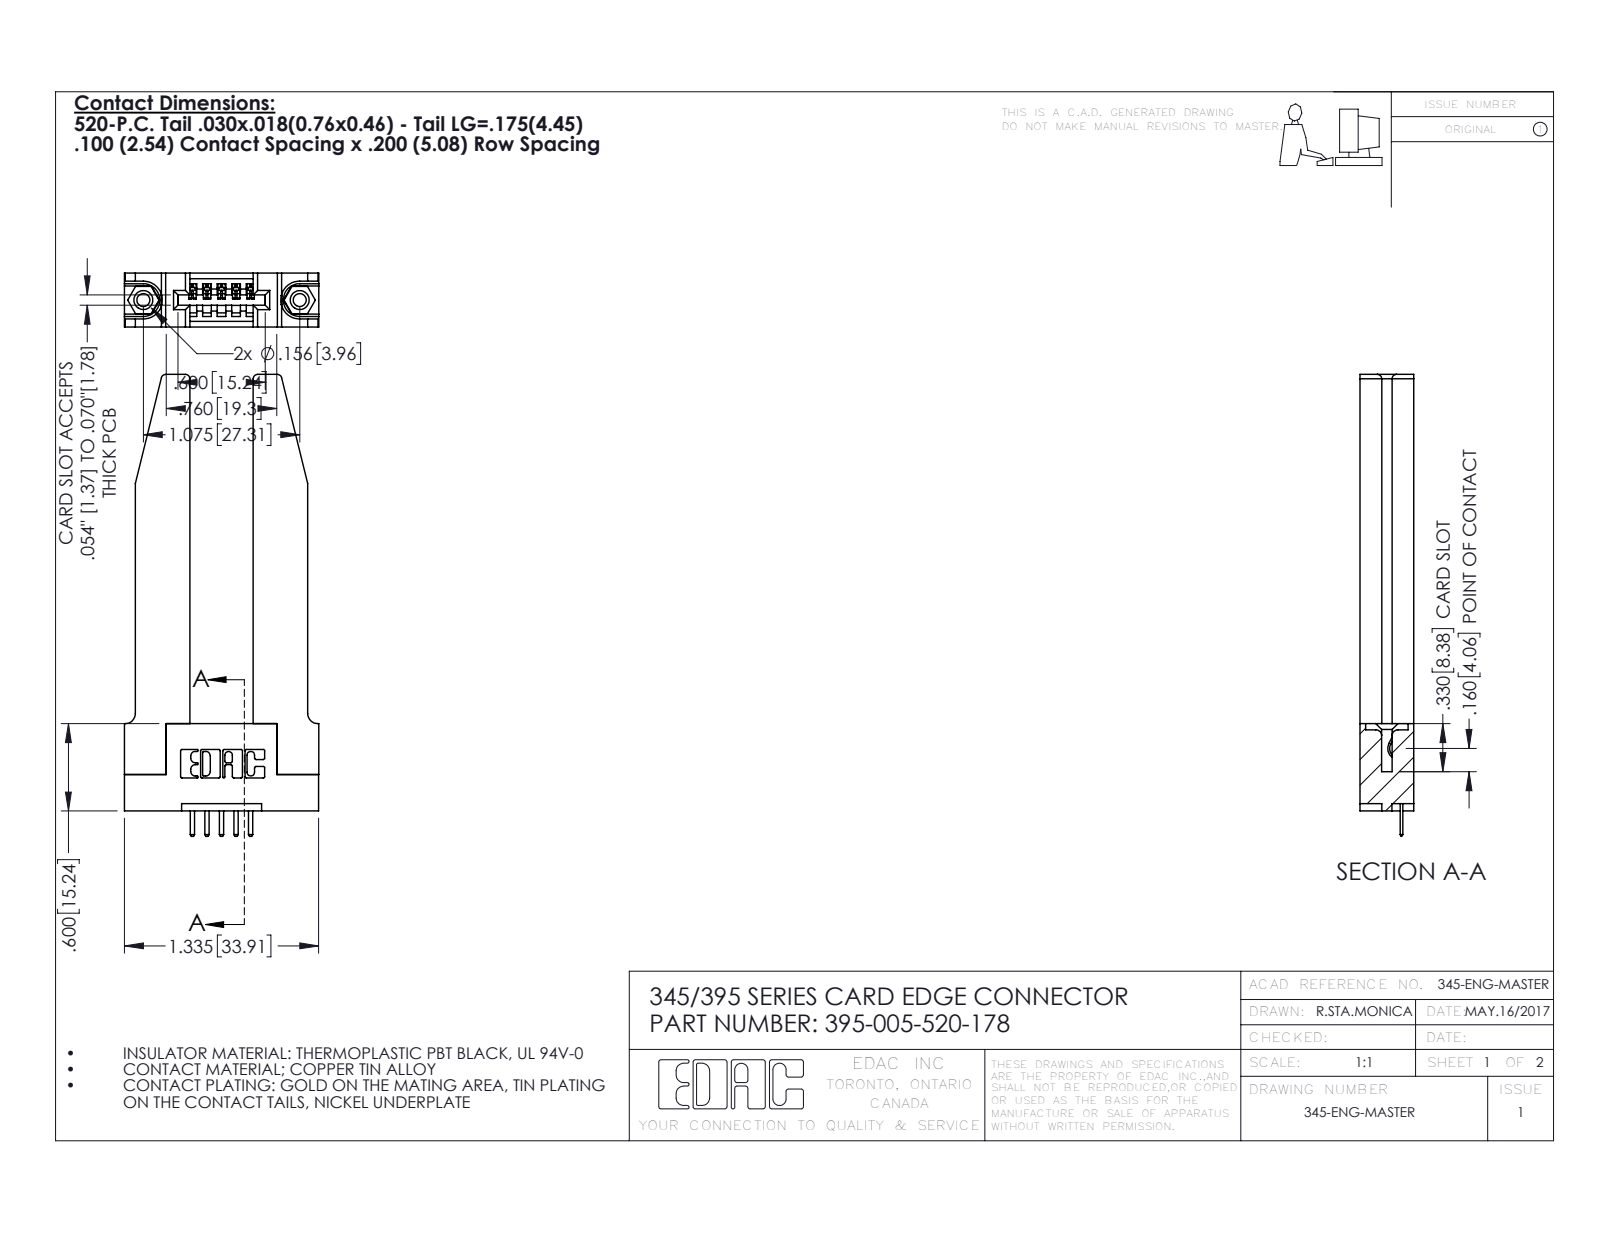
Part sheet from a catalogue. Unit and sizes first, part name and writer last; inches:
Units: inches
Overall size (bounding box): 3.175 × 1.336 × 0.37
Round holes (diameter × count): ⌀0.089 ×2, ⌀0.125 ×2, ⌀0.156 ×2, ⌀0.064 ×1
Round bosses / shafts (diameter × count): ⌀0.155 ×2
Partial cylindrical surfaces — rounded edges, fillets, slot ends (radius × count): R0.01 ×22, R0.01 ×12, R0.006 ×10, R0.03 ×8, R0.007 ×6, R0.031 ×6, R0.026 ×3, R0.031 ×2
Main face-to-face distances: 0.37, 0.15, 0.22, 0.435, 0.148, 0.072, 0.2, 0.077, 0.298, 0.095
Hole centre spacings: 0.27, 0.847, 1.075
Volume: 0.651 in³ · Surface area: 15.74 in²
Bodies: 10 solids, 670 faces (432 planar, 186 cylindrical, 52 other)
Part name (STEP PRODUCT): 345-250-001_345-250-001-102; 395-005-520-178; 345 Part_Flush Mounting Lugs - 0.156 Dia-TH; 345-292-001_345-293-120 (+1 more)
STEP written by: SolidWorks 2016 (CONFIG_CONTROL_DESIGN)
